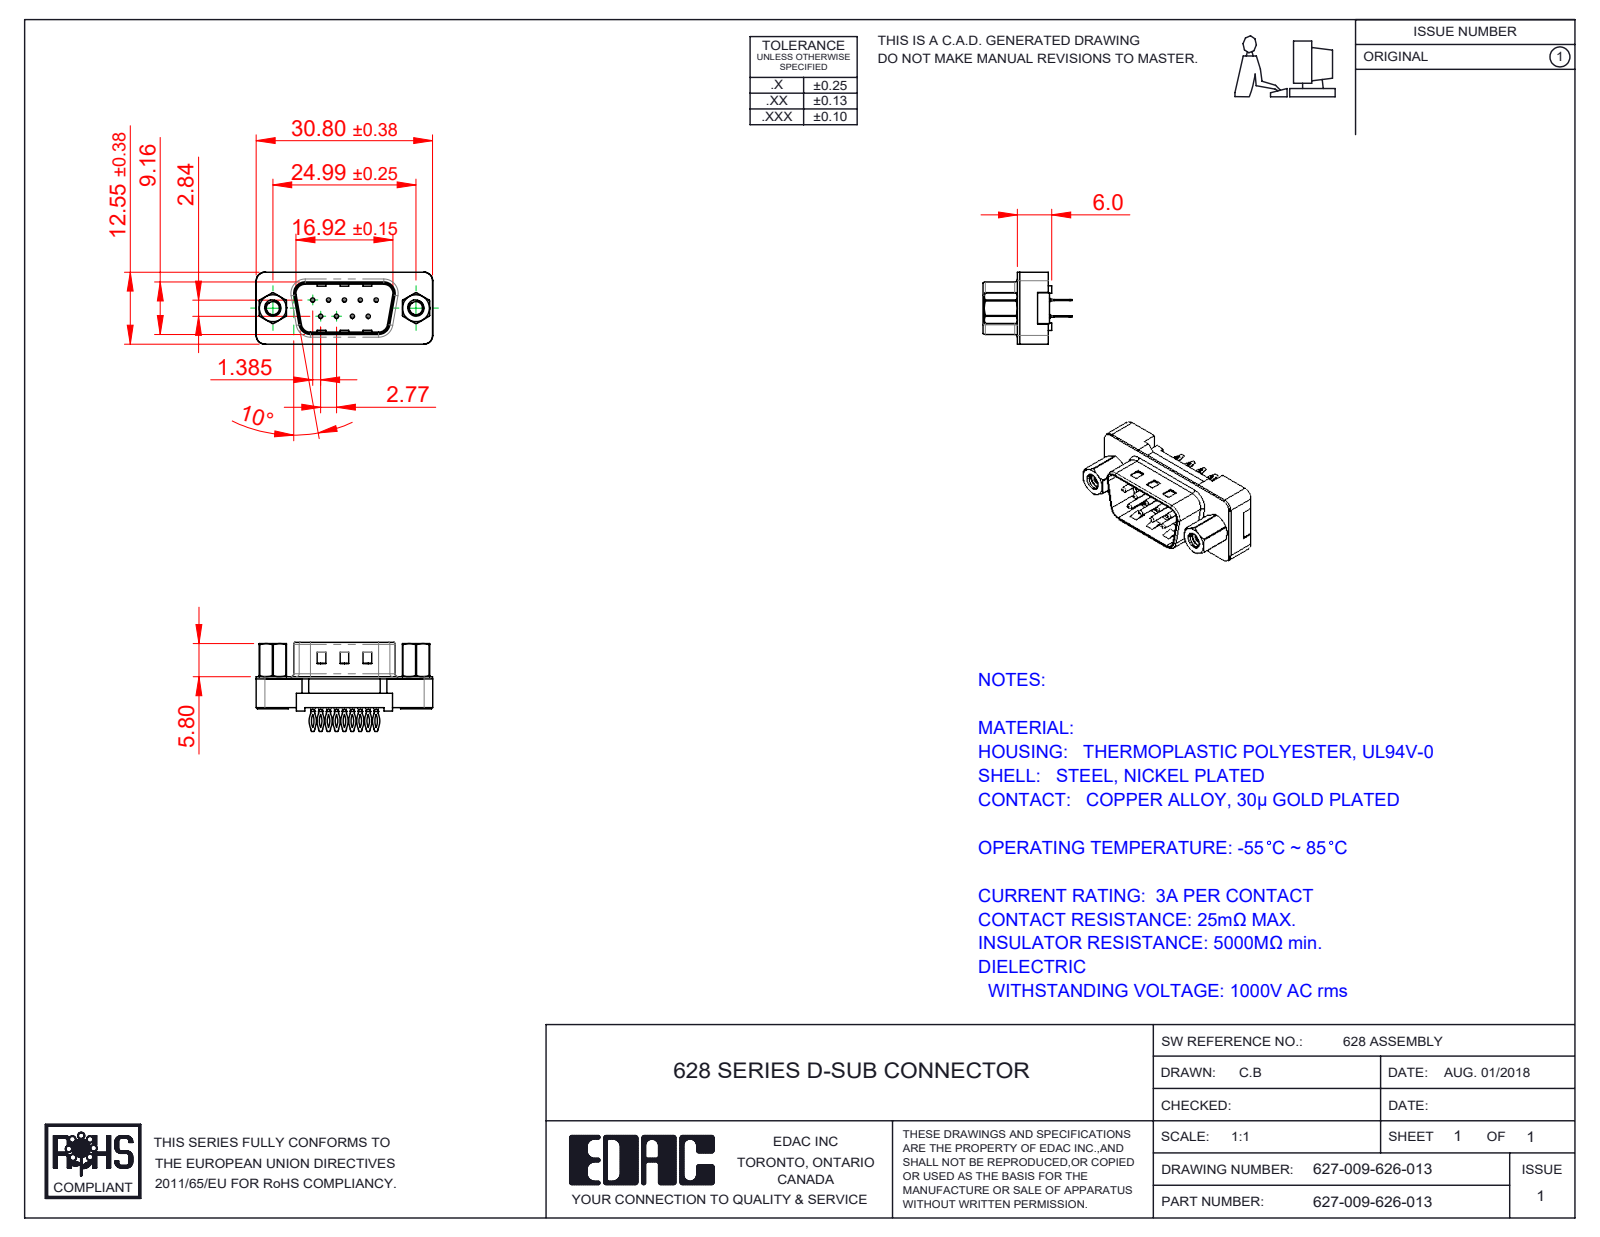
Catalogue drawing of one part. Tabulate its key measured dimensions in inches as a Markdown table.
| quantity | value |
| --- | --- |
| part name | 627 PB Contact Row 1_26; 627-009-626-013; 627 4-40 Hex Standoff; 627 PB Shell_09 Contacts (+3 more) |
| STEP written by | SolidWorks 2020 (CONFIG_CONTROL_DESIGN) |
| units | inches |
| bodies | 15 solids, 1026 faces (548 planar, 348 cylindrical, 130 other) |
| overall size | 1.213 × 0.612 × 0.494 |
| volume | 0.113 in³ |
| surface area | 5.949 in² |
| round holes (diameter × count) | 0.014 × 9, 0.033 × 9, 0.089 × 2, 0.09 × 2, 0.157 × 2, 0.189 × 2, 0.197 × 2 |
| round bosses / shafts (diameter × count) | 0.03 × 9, 0.193 × 2, 0.11 × 2 |
| partial cylindrical surfaces (radius × count) | 0.01 × 18, 0.115 × 18, 0.131 × 18, 0.005 × 9, 0.02 × 8, 0.059 × 7, 0.035 × 4, 0.063 × 4 |
| main face-to-face distances | 0.016, 0.098, 0.213, 0.197, 0.114, 0.345, 0.083, 0.094, 0.256, 0.027 |
| hole center spacings | 0.124, 0.109, 0.198, 0.218, 0.295, 0.198, 0.279, 0.327 |
